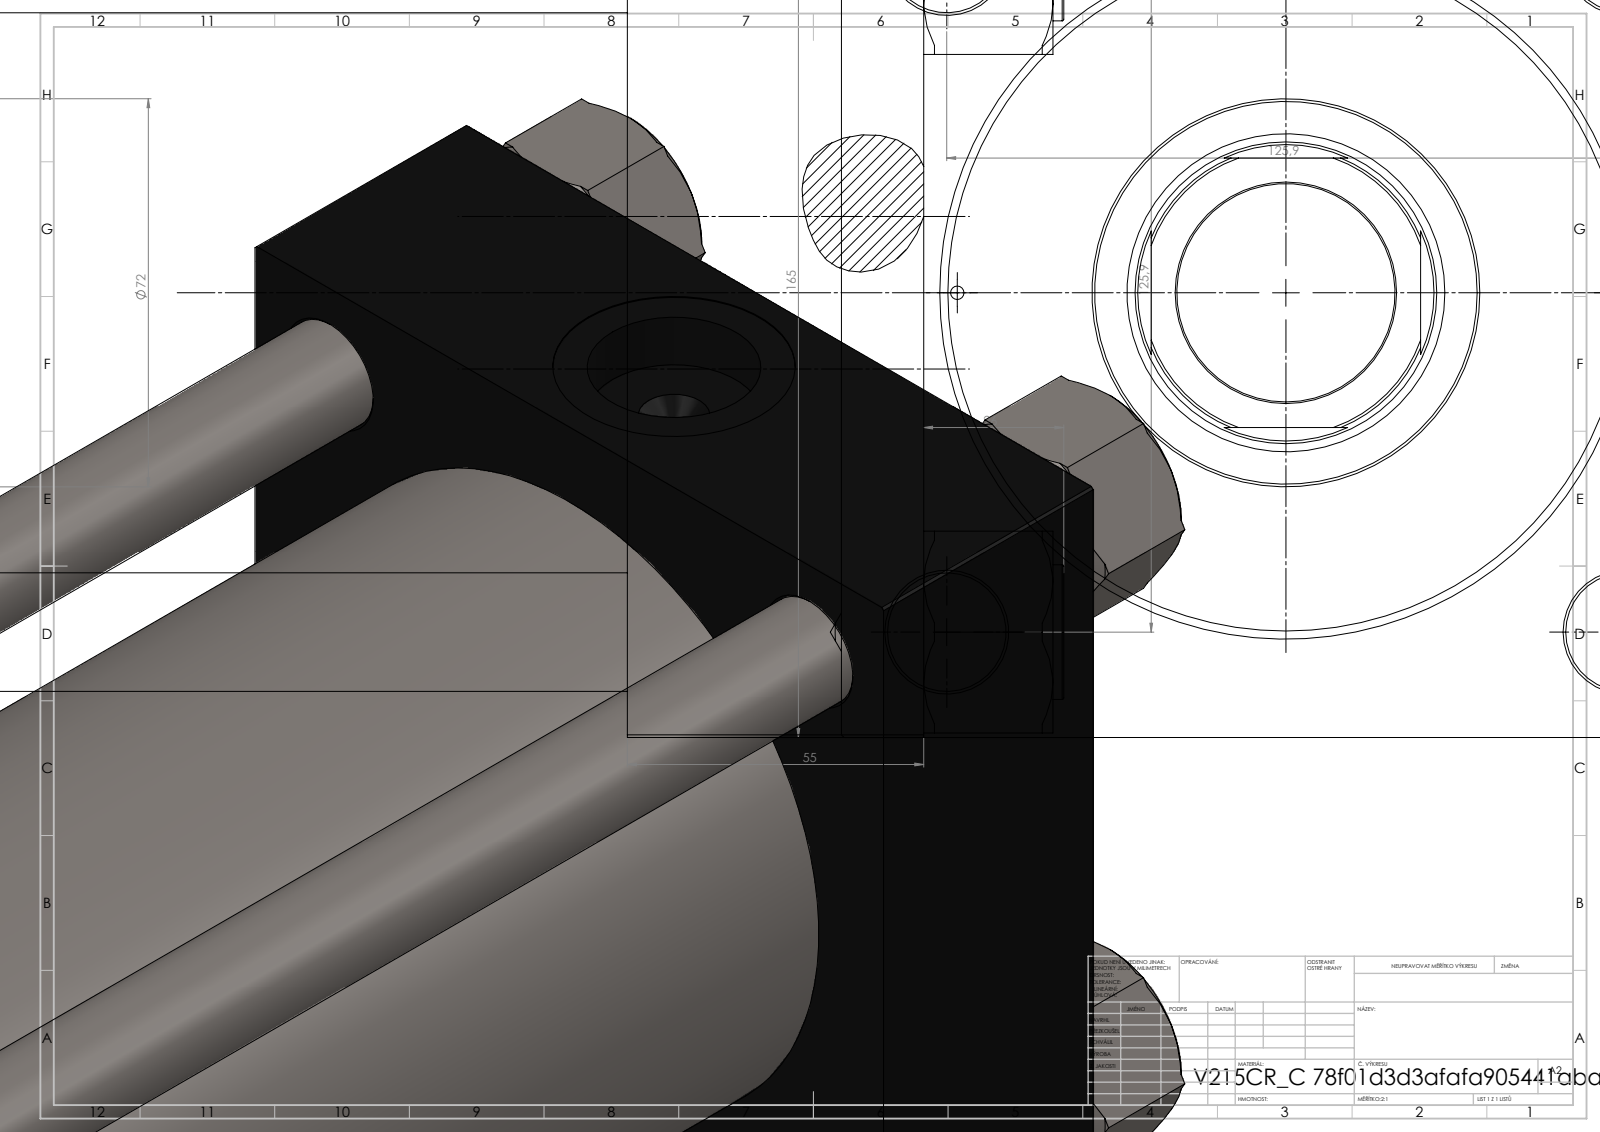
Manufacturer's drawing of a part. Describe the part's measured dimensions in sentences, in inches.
The part is named "V215CR_C_TYCINKA; V215_VC_A; V215CR_C_Body; MSRF_MSRG1 (+2 more)". Its 3-D file was written by "SolidWorks 2019 (CONFIG_CONTROL_DESIGN)". It is 12 solids with 1235 faces: 594 planar, 105 cylindrical and 536 other. Overall it measures 20 by 6.752 by 6.496 inches. Its volume is 347.3 cubic inches and its surface area 1 233 square inches. Round holes: 4 of diameter 0.866, 2 of diameter 0.098, 2 of diameter 0.276, 2 of diameter 1.269, 2 of diameter 1.772, 1 of diameter 1.594, 1 of diameter 2.205, 1 of diameter 2.323, 1 of diameter 3.78, 1 of diameter 4.921, 1 of diameter 4.941. Round bosses or shafts: 4 of diameter 0.984, 1 of diameter 5.157, 1 of diameter 2.835, 1 of diameter 0.197, 1 of diameter 0.098. Partial cylindrical surfaces (rounded edges, fillets, slot ends): 6 of radius 0.02, 2 of radius 0.236, 1 of radius 1.063. The main face-to-face distances are 6.496, 2.165, 17.598, 15.433, 14.528, 12.362, 3.071, 16.469, 14.303, 1.941. The hole center spacings are 2.48, 3.505, 4.957, 5.473, 2.402, 7.01, 4.803, 14.508.
